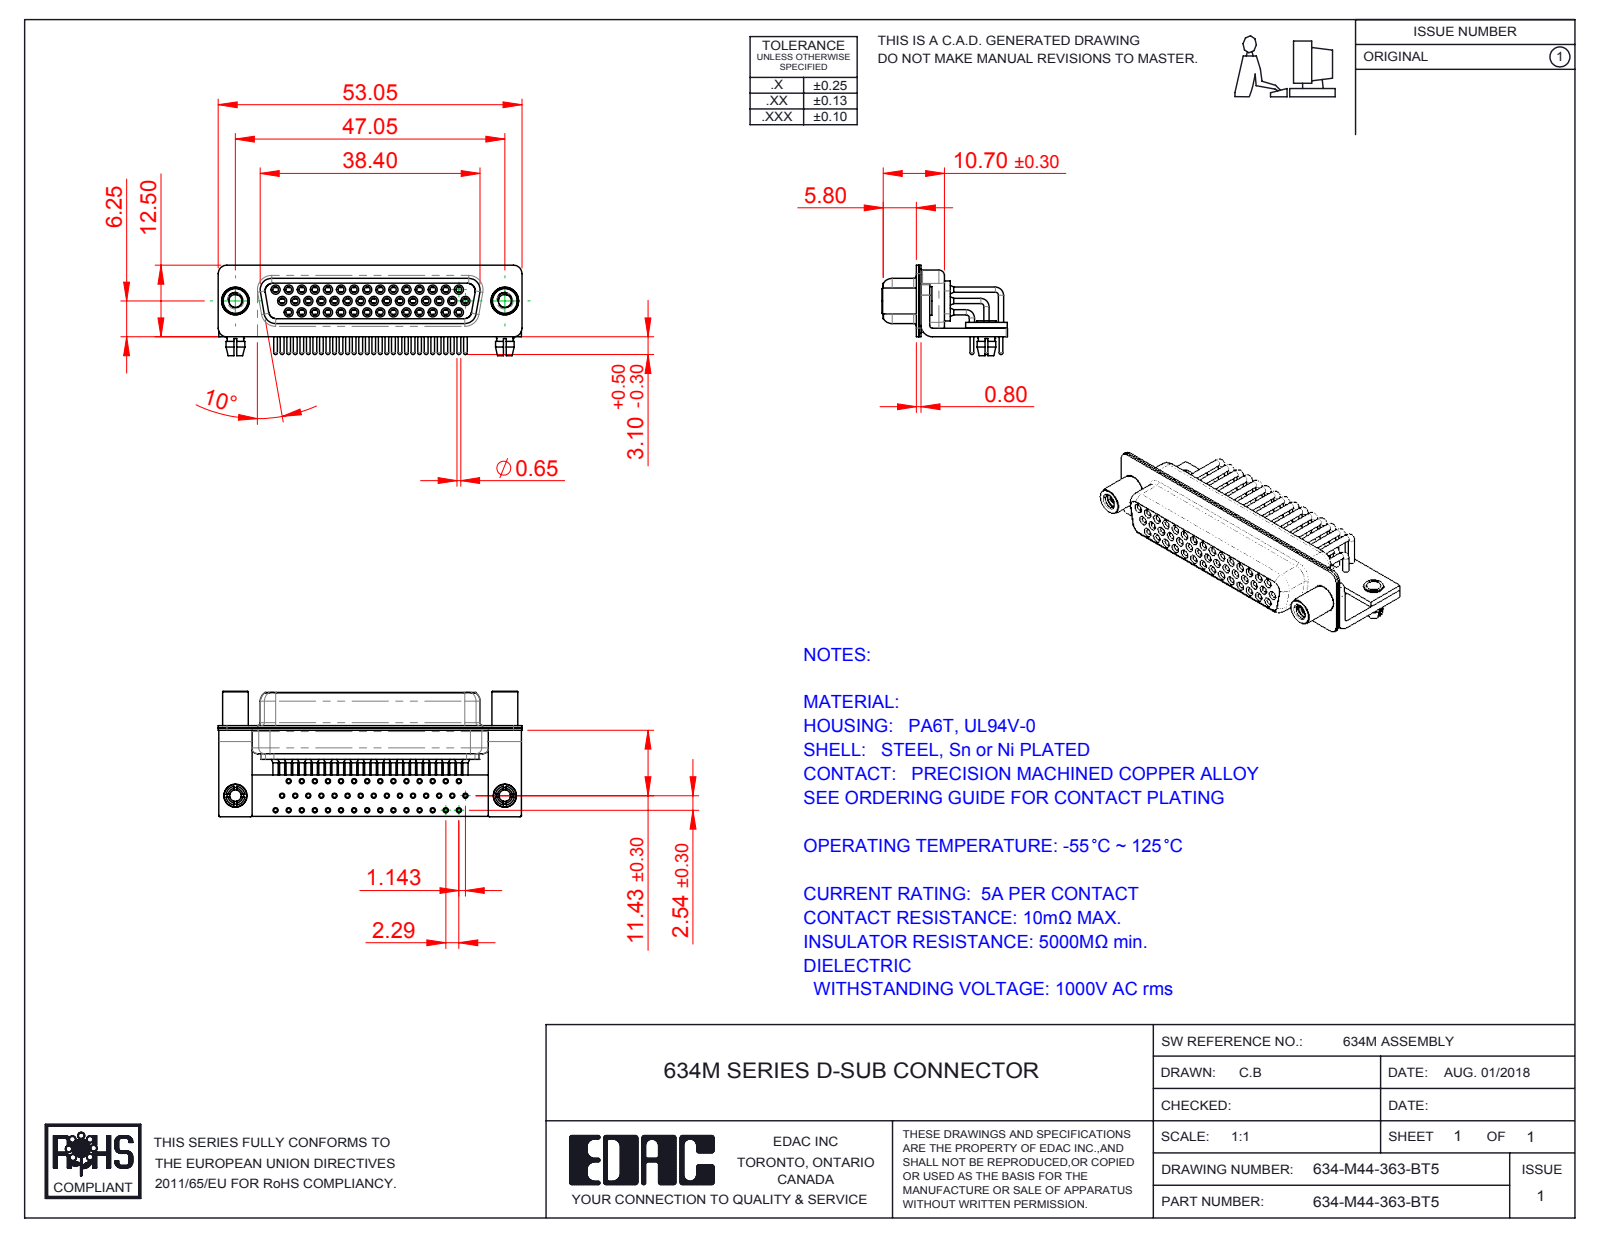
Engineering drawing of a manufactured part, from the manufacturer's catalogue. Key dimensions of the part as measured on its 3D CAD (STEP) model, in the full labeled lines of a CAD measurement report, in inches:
Part name (STEP PRODUCT): 634M Stabilizer Board_44 Contacts; 634M Board Lock; 634M Shell Rear_44 Contacts; 634M Housing_44 Contacts (+7 more)
STEP written by: SolidWorks 2016 (CONFIG_CONTROL_DESIGN)
Units: inches
Bodies: 54 solids, 2891 faces (803 planar, 1333 cylindrical, 755 other)
Overall size (bounding box): 2.089 × 0.862 × 0.622
Volume: 0.283 in³ · Surface area: 23.49 in²
Round holes (diameter × count): ⌀0.079 ×46, ⌀0.035 ×44, ⌀0.039 ×44, ⌀0.043 ×44, ⌀0.067 ×44, ⌀0.071 ×44, ⌀0.089 ×2, ⌀0.098 ×2, ⌀0.126 ×2, ⌀0.157 ×2, ⌀0.189 ×2
Round bosses / shafts (diameter × count): ⌀0.063 ×44, ⌀0.059 ×44, ⌀0.035 ×44, ⌀0.026 ×44, ⌀0.197 ×2, ⌀0.193 ×2, ⌀0.177 ×2, ⌀0.157 ×2
Partial cylindrical surfaces — rounded edges, fillets, slot ends (radius × count): R0.01 ×16, R0.059 ×16, R0.079 ×13, R0.053 ×8, R0.063 ×8, R0.02 ×5, R0.024 ×4, R0.026 ×4
Main face-to-face distances: 0.016, 0.091, 0.075, 0.039, 0.031, 0.368, 0.335, 0.059, 0.057, 0.352
Hole centre spacings: 0.09, 0.09, 0.18, 0.27, 0.45, 0.156, 0.324, 0.36
